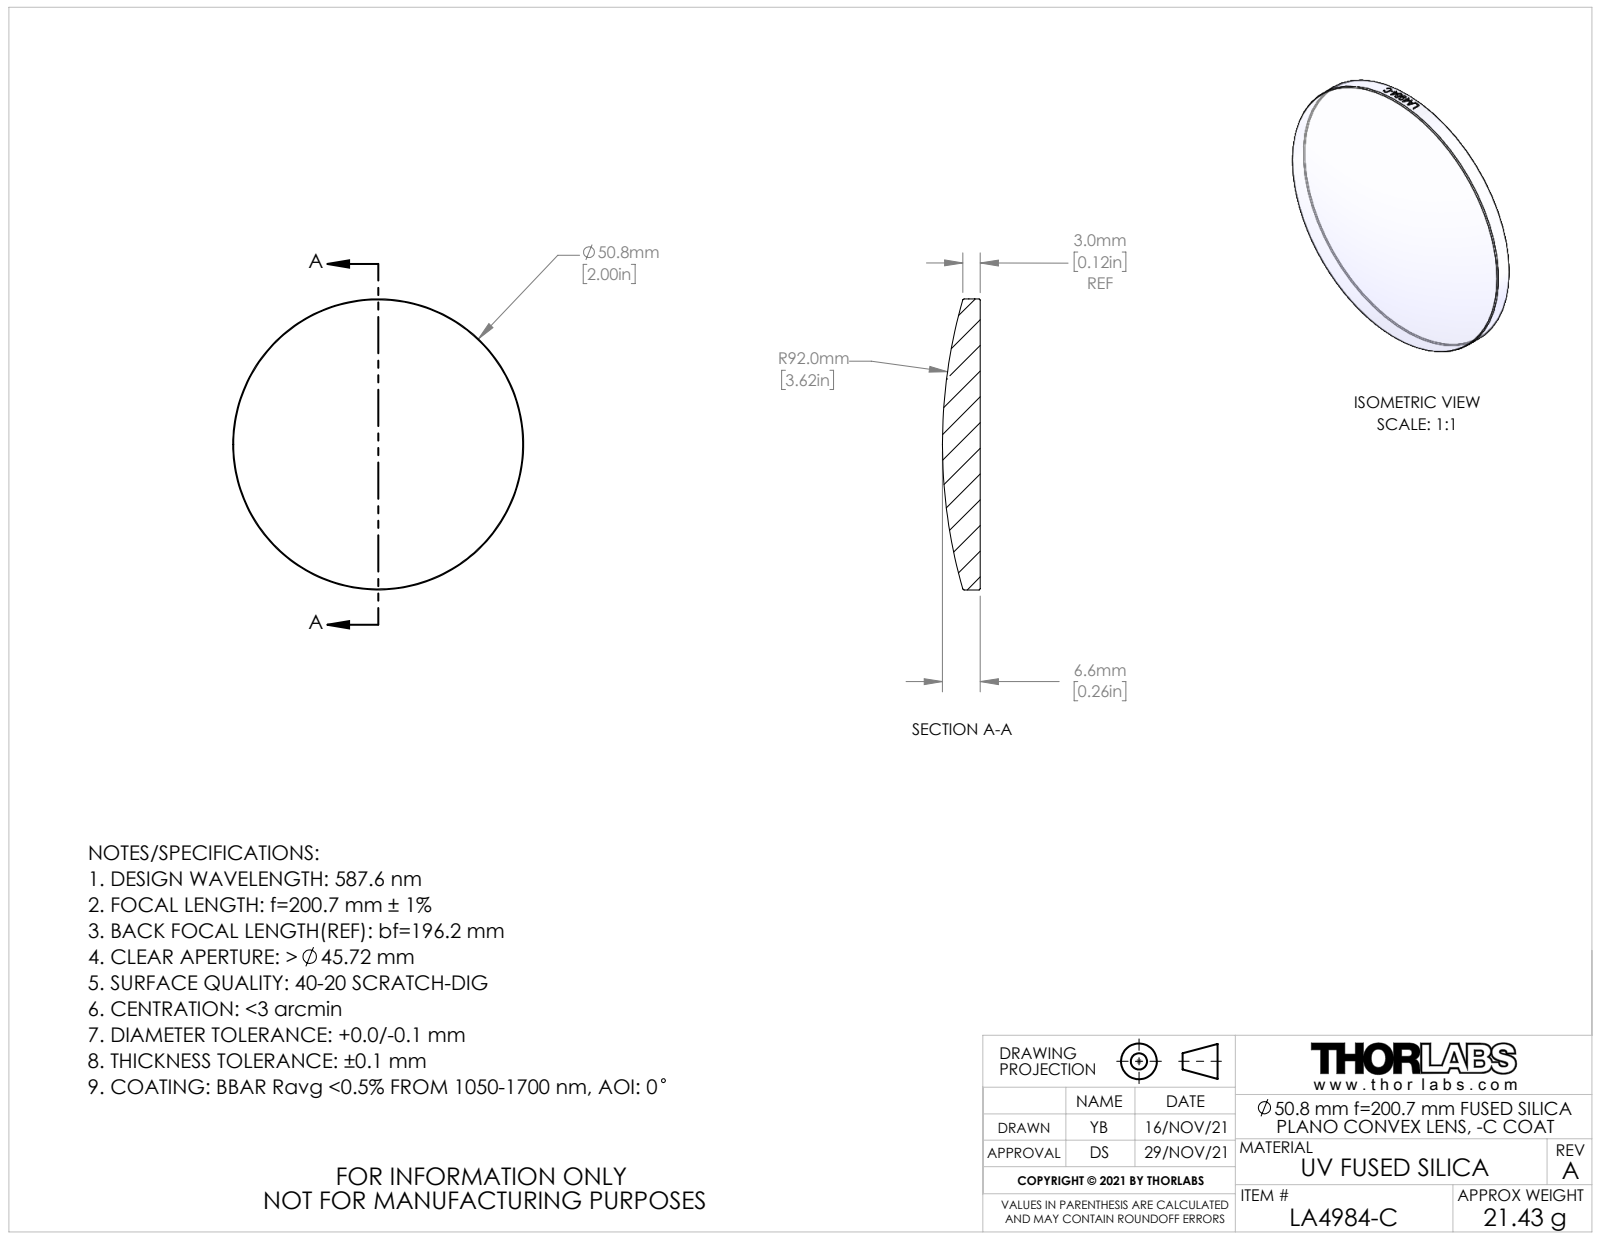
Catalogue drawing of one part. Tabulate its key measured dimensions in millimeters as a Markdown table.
| quantity | value |
| --- | --- |
| part name | CTN018076-E0W; CTN018145 |
| STEP written by | SolidWorks 2018 (AUTOMOTIVE_DESIGN) |
| units | millimeters |
| bodies | 1 solid, 23 faces (1 planar, 16 cylindrical, 6 other) |
| overall size | 50.8 × 50.8 × 6.58 |
| volume | 9 726 mm³ |
| surface area | 4 544 mm² |
| round bosses / shafts (diameter × count) | 50.8 × 1 |
